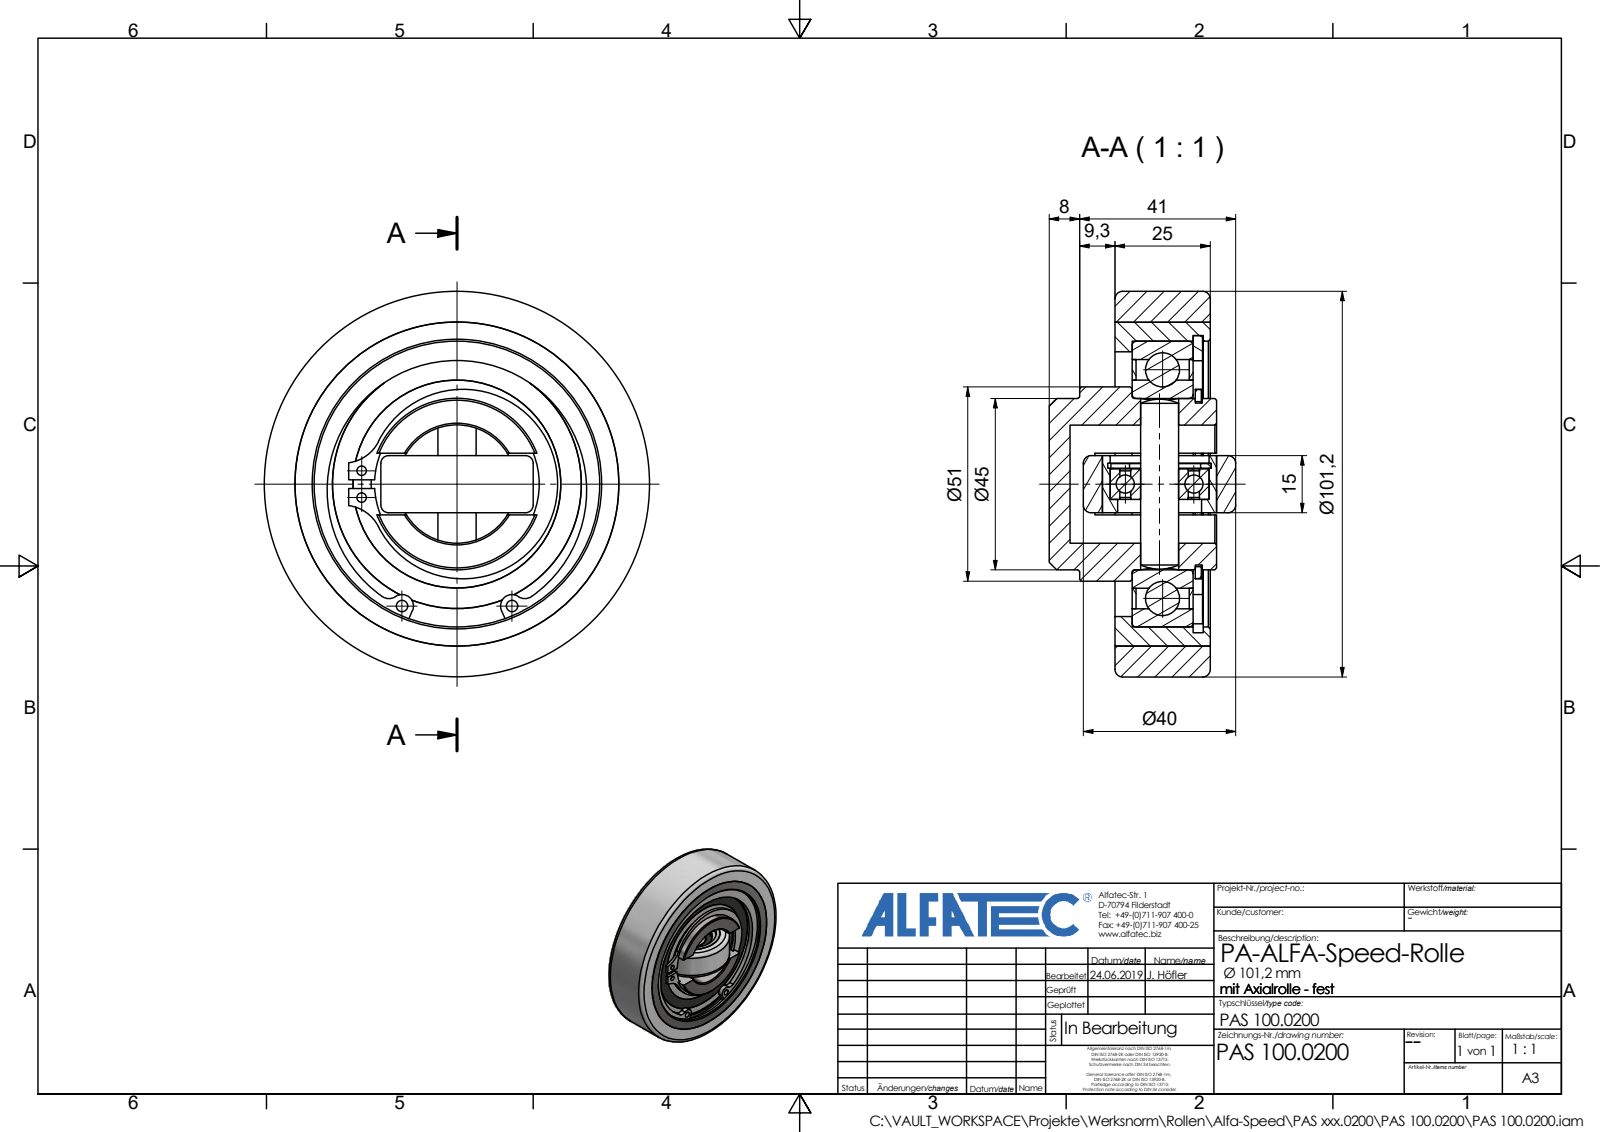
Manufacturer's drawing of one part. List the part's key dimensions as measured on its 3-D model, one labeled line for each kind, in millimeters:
Part name (STEP PRODUCT): PAS 100.0200_Kontur
STEP written by: Autodesk Inventor 2020 (AP242_MANAGED_MODEL_BASED_3D_ENGINEERING_MIM_LF)
Units: millimetres
Bodies: 1 solid, 47 faces (22 planar, 12 cylindrical, 13 other)
Overall size (bounding box): 101.2 × 101.2 × 49
Volume: 222 927 mm³ · Surface area: 29 122 mm²
Round holes (diameter × count): ⌀31 ×1
Round bosses / shafts (diameter × count): ⌀101.2 ×1, ⌀51 ×1, ⌀45 ×1
Partial cylindrical surfaces — rounded edges, fillets, slot ends (radius × count): R13 ×1, R13.6 ×1, R20 ×1
Main face-to-face distances: 25, 17.3, 42.3, 44, 26.7, 1.7, 12, 5.3, 30.3, 32
